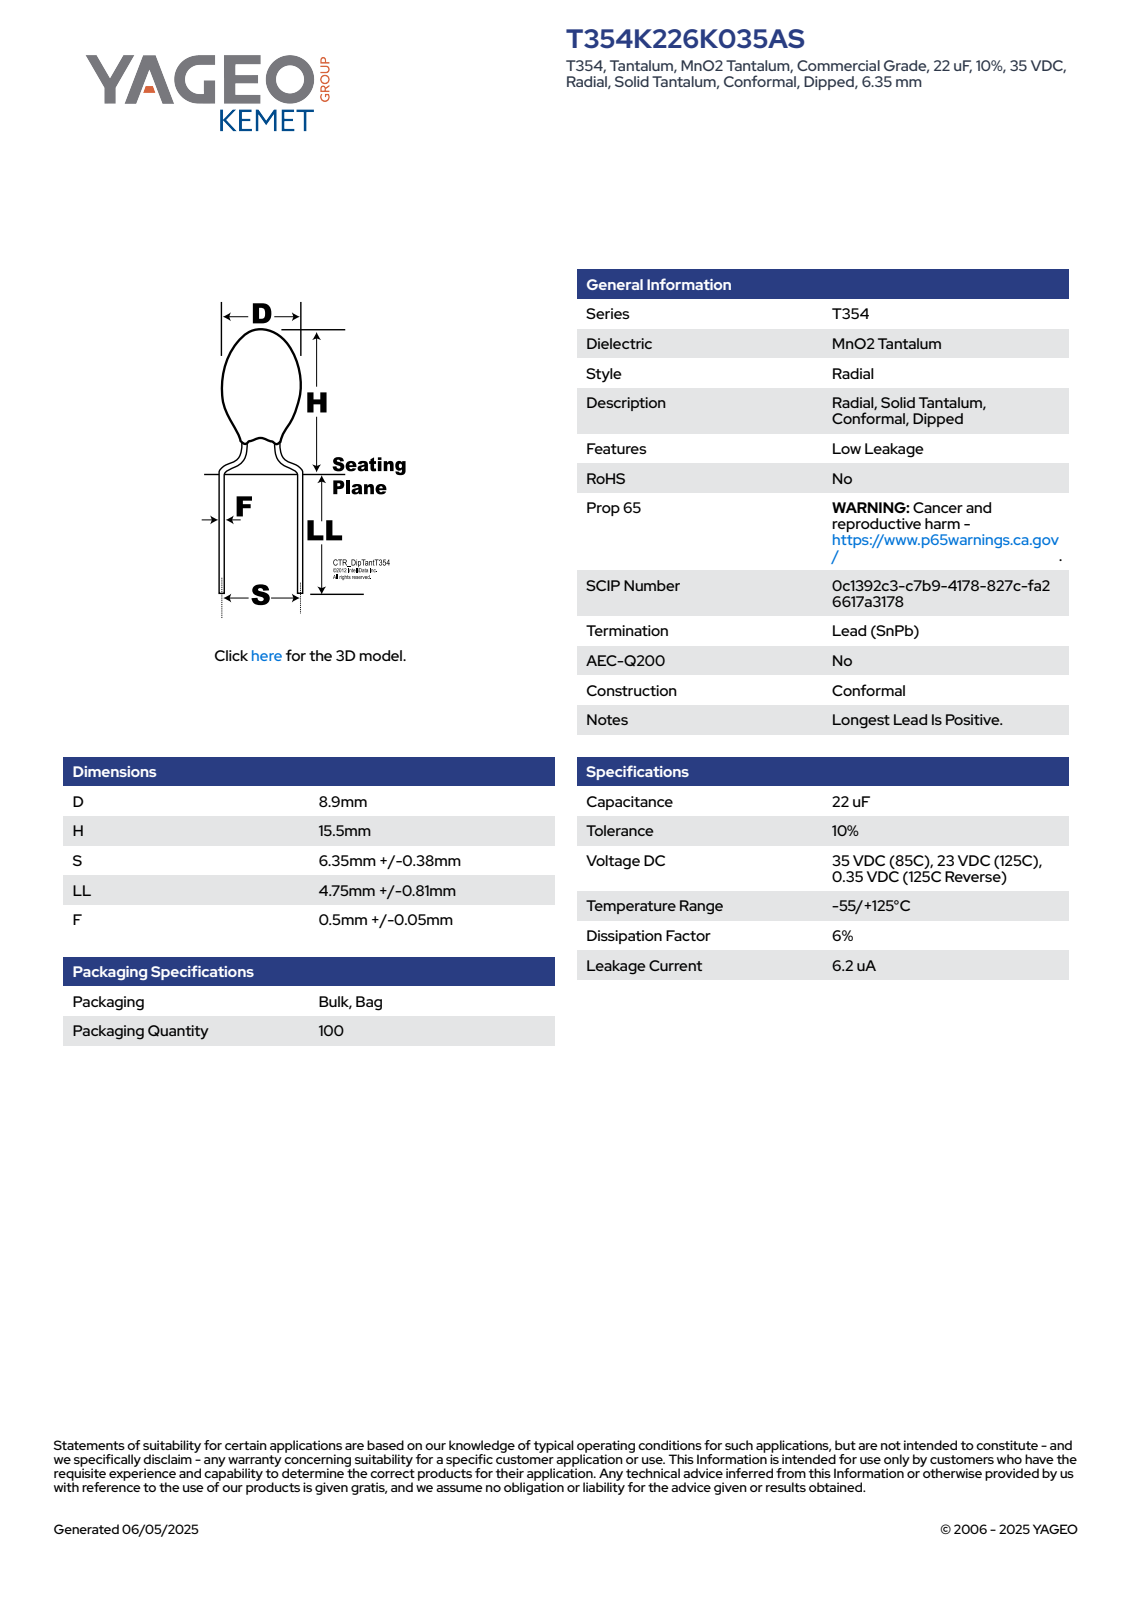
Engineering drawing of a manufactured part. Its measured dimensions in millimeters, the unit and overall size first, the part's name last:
Units: millimetres
Overall size (bounding box): 21.06 × 8.9 × 8.9
Round bosses / shafts (diameter × count): ⌀0.55 ×2, ⌀8.9 ×1
Partial cylindrical surfaces — rounded edges, fillets, slot ends (radius × count): R4.44 ×1
Main face-to-face distances: 10.81, 10.25, 21.06, 17.2, 6.95, 3.86, 16.19, 5.94, 1.01, 4.87
Volume: 573 mm³ · Surface area: 381 mm²
Bodies: 1 solid, 81 faces (26 planar, 10 cylindrical, 45 other)
Part name (STEP PRODUCT): CTR_T354_D8.9H15.5S6.35LL5.56F0.55
STEP written by: SolidWorks 2014 (AUTOMOTIVE_DESIGN)
